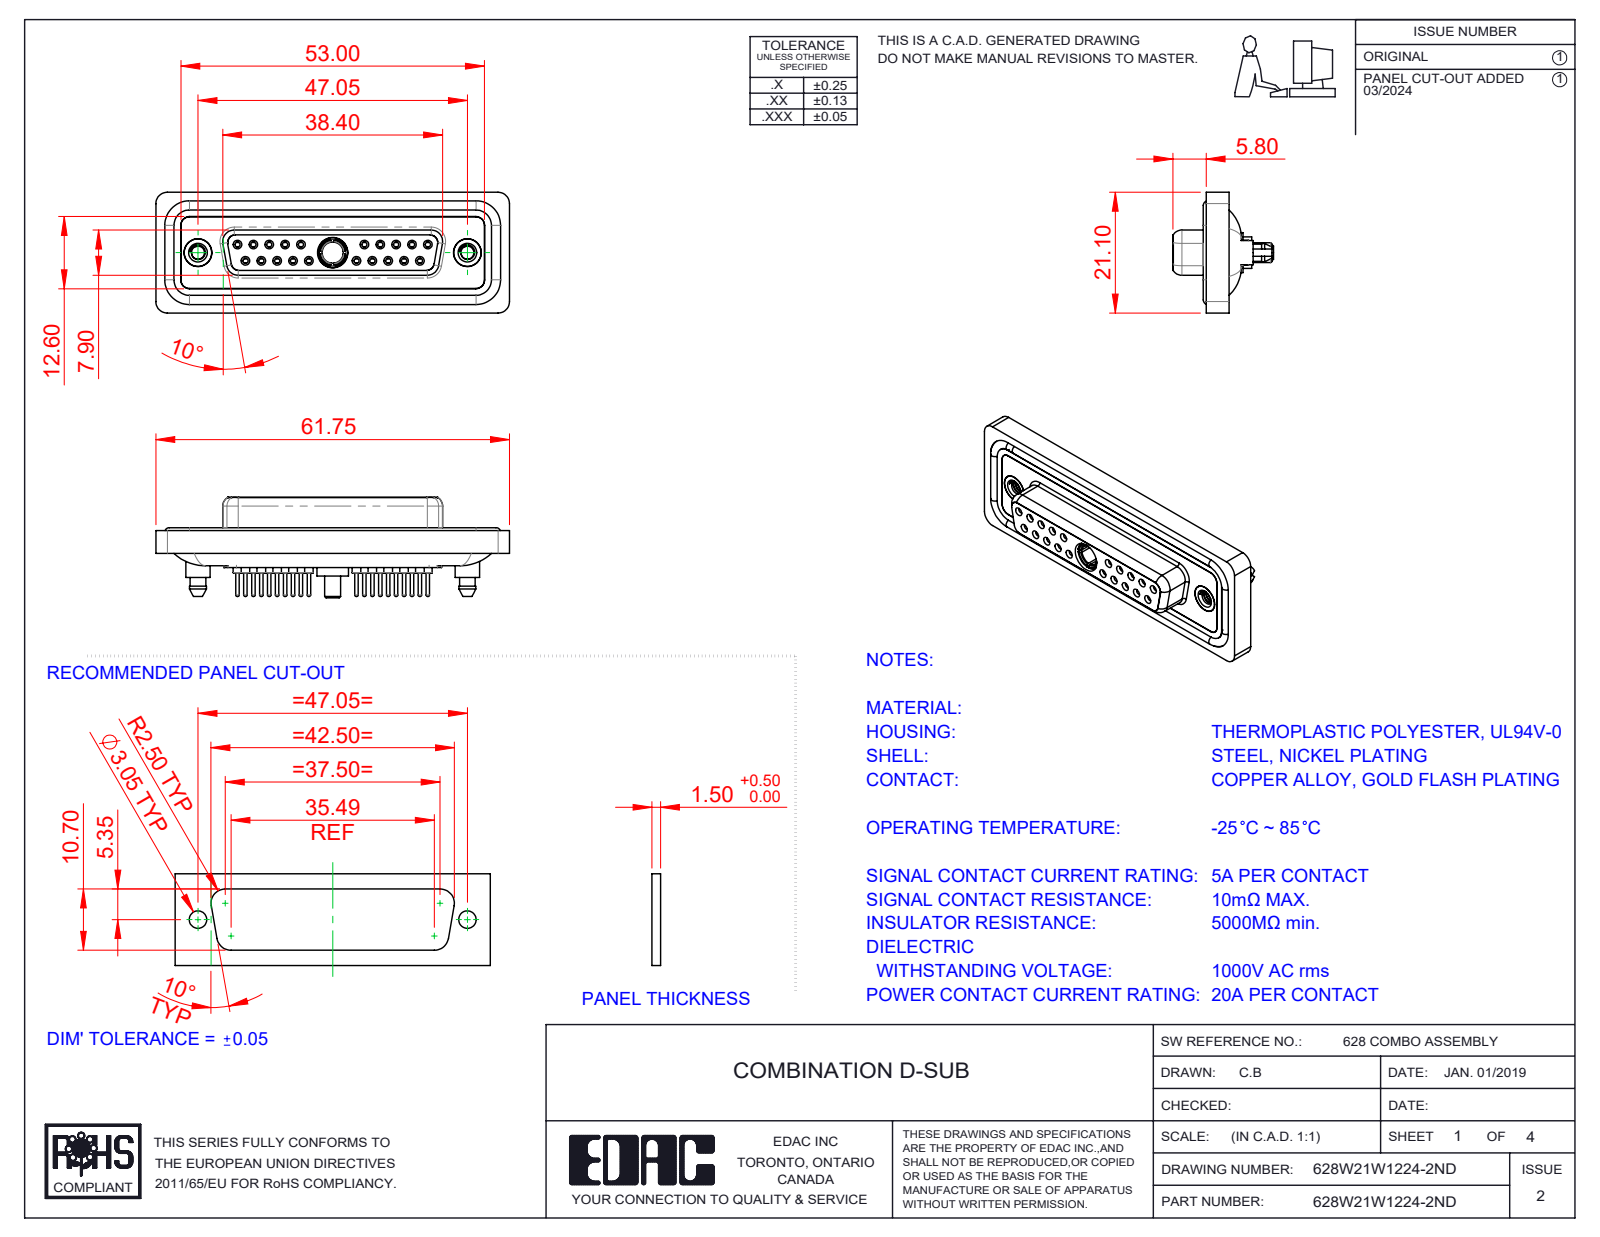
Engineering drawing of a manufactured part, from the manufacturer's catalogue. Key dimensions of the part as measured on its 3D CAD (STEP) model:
Part name (STEP PRODUCT): 628Combo Contact Row 2_24; 628Combo Shell Front_25 Contacts; 628Combo Shell Rear_25 Contacts; Power Socket_20A S (+5 more)
STEP written by: SolidWorks 2023 (CONFIG_CONTROL_DESIGN)
Units: millimetres
Bodies: 29 solids, 1626 faces (450 planar, 639 cylindrical, 537 other)
Overall size (bounding box): 61.75 × 21.1 × 17.55
Volume: 8 509 mm³ · Surface area: 14 341 mm²
Round holes (diameter × count): ⌀0.9 ×20, ⌀1.1 ×20, ⌀1.5 ×20, ⌀2 ×20, ⌀1.6 ×10, ⌀1.7 ×10, ⌀4.85 ×3, ⌀2.26 ×2, ⌀4 ×2, ⌀4.05 ×2, ⌀5 ×2, ⌀3.7 ×1
Round bosses / shafts (diameter × count): ⌀2.2 ×20, ⌀0.6 ×20, ⌀1.6 ×14, ⌀5.4 ×2, ⌀4.95 ×2, ⌀4.8 ×2, ⌀4.25 ×2, ⌀5.5 ×1
Partial cylindrical surfaces — rounded edges, fillets, slot ends (radius × count): R1.5 ×24, R2 ×18, R1.6 ×10, R1.35 ×8, R0.25 ×4, R0.5 ×4, R0.6 ×4, R0.65 ×4
Main face-to-face distances: 0.4, 1.8, 7.45, 6.6, 5.65, 1.6, 0.5, 7.05, 2.9, 1.1
Hole centre spacings: 3.16, 2.77, 5.54, 5.03, 8.31, 7.48, 16.62, 19.39
